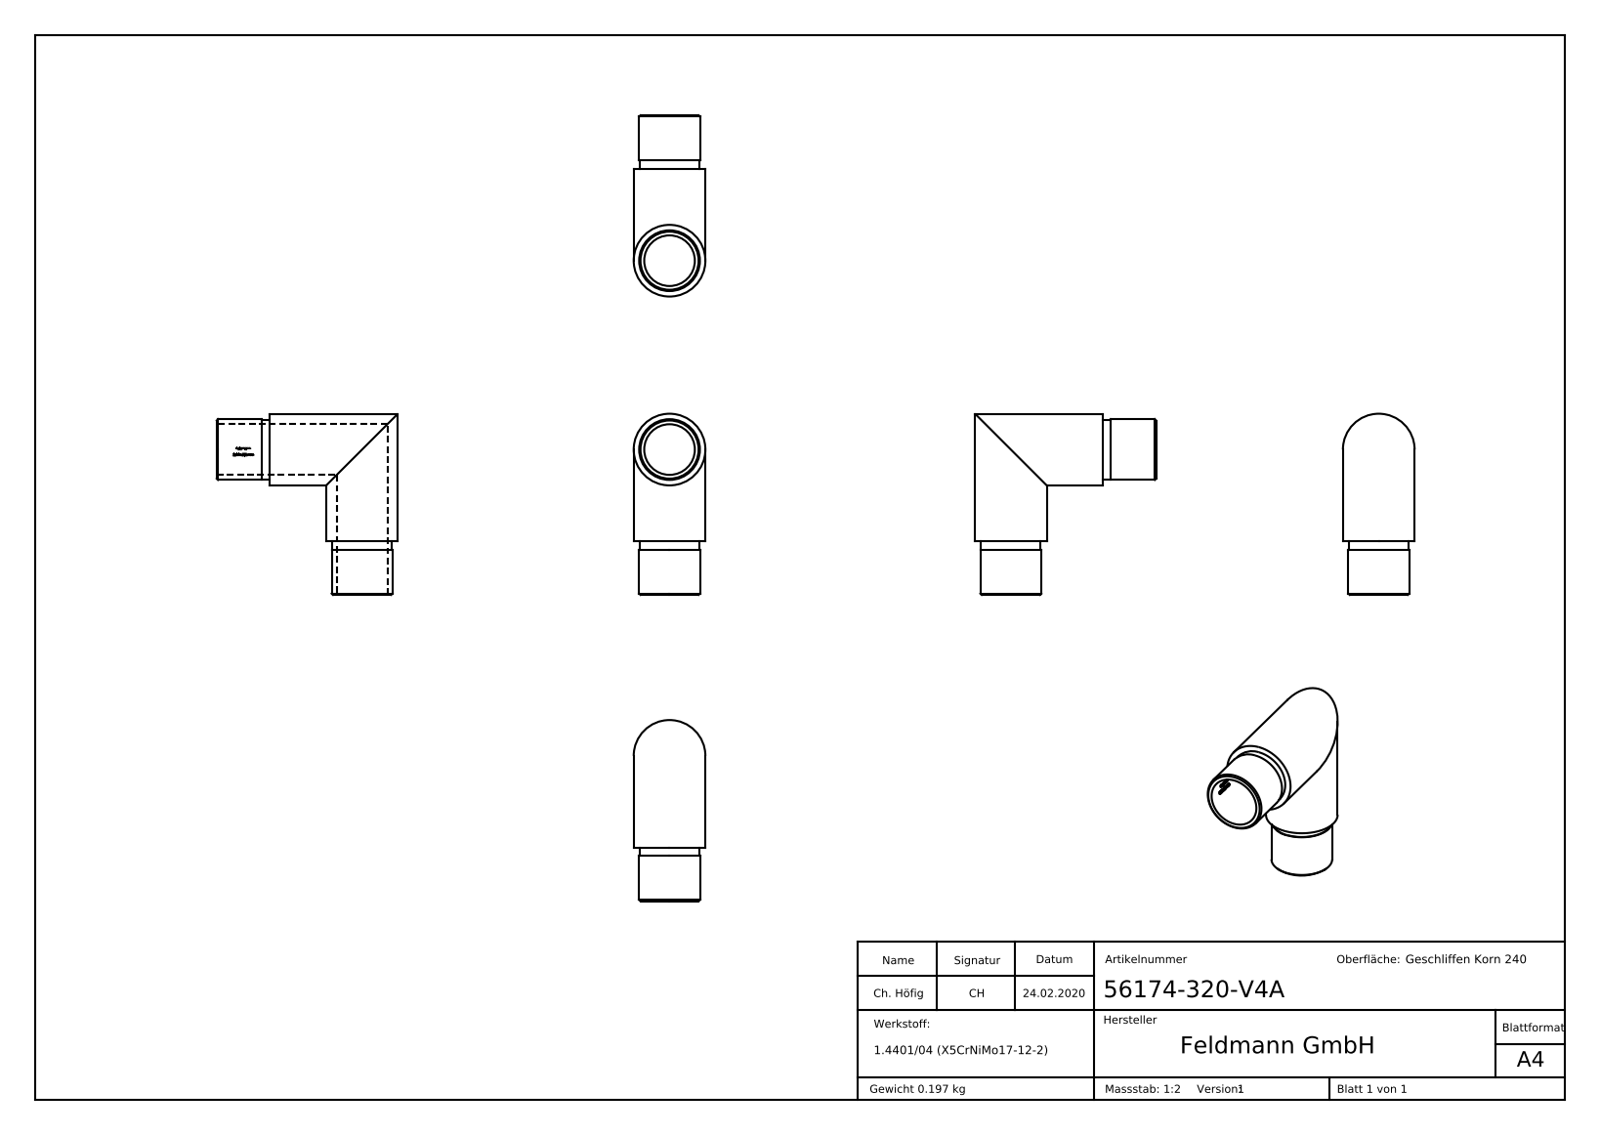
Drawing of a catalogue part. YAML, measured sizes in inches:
part_name: "56174-320-V4A"
step_written_by: "SolidWorks 2015 (CONFIG_CONTROL_DESIGN)"
units: inches
bodies: {solids: 1, faces: 275, planar: 142, cylindrical: 37, other: 96}
overall_size: [2.677, 2.677, 1.059]
volume: 1.499
surface_area: 24.49
round_holes:
  - {diameter: 0.748, count: 2}
round_bosses_or_shafts:
  - {diameter: 1.059, count: 2}
  - {diameter: 0.898, count: 2}
  - {diameter: 0.882, count: 2}
partial_cylinders:
  - {radius: 0.378, count: 1}
face_to_face_distances: [0.787, 0.669, 0.118, 0.021, 0.042, 0.031, 0.018, 0.039, 0.091, 0.103]
